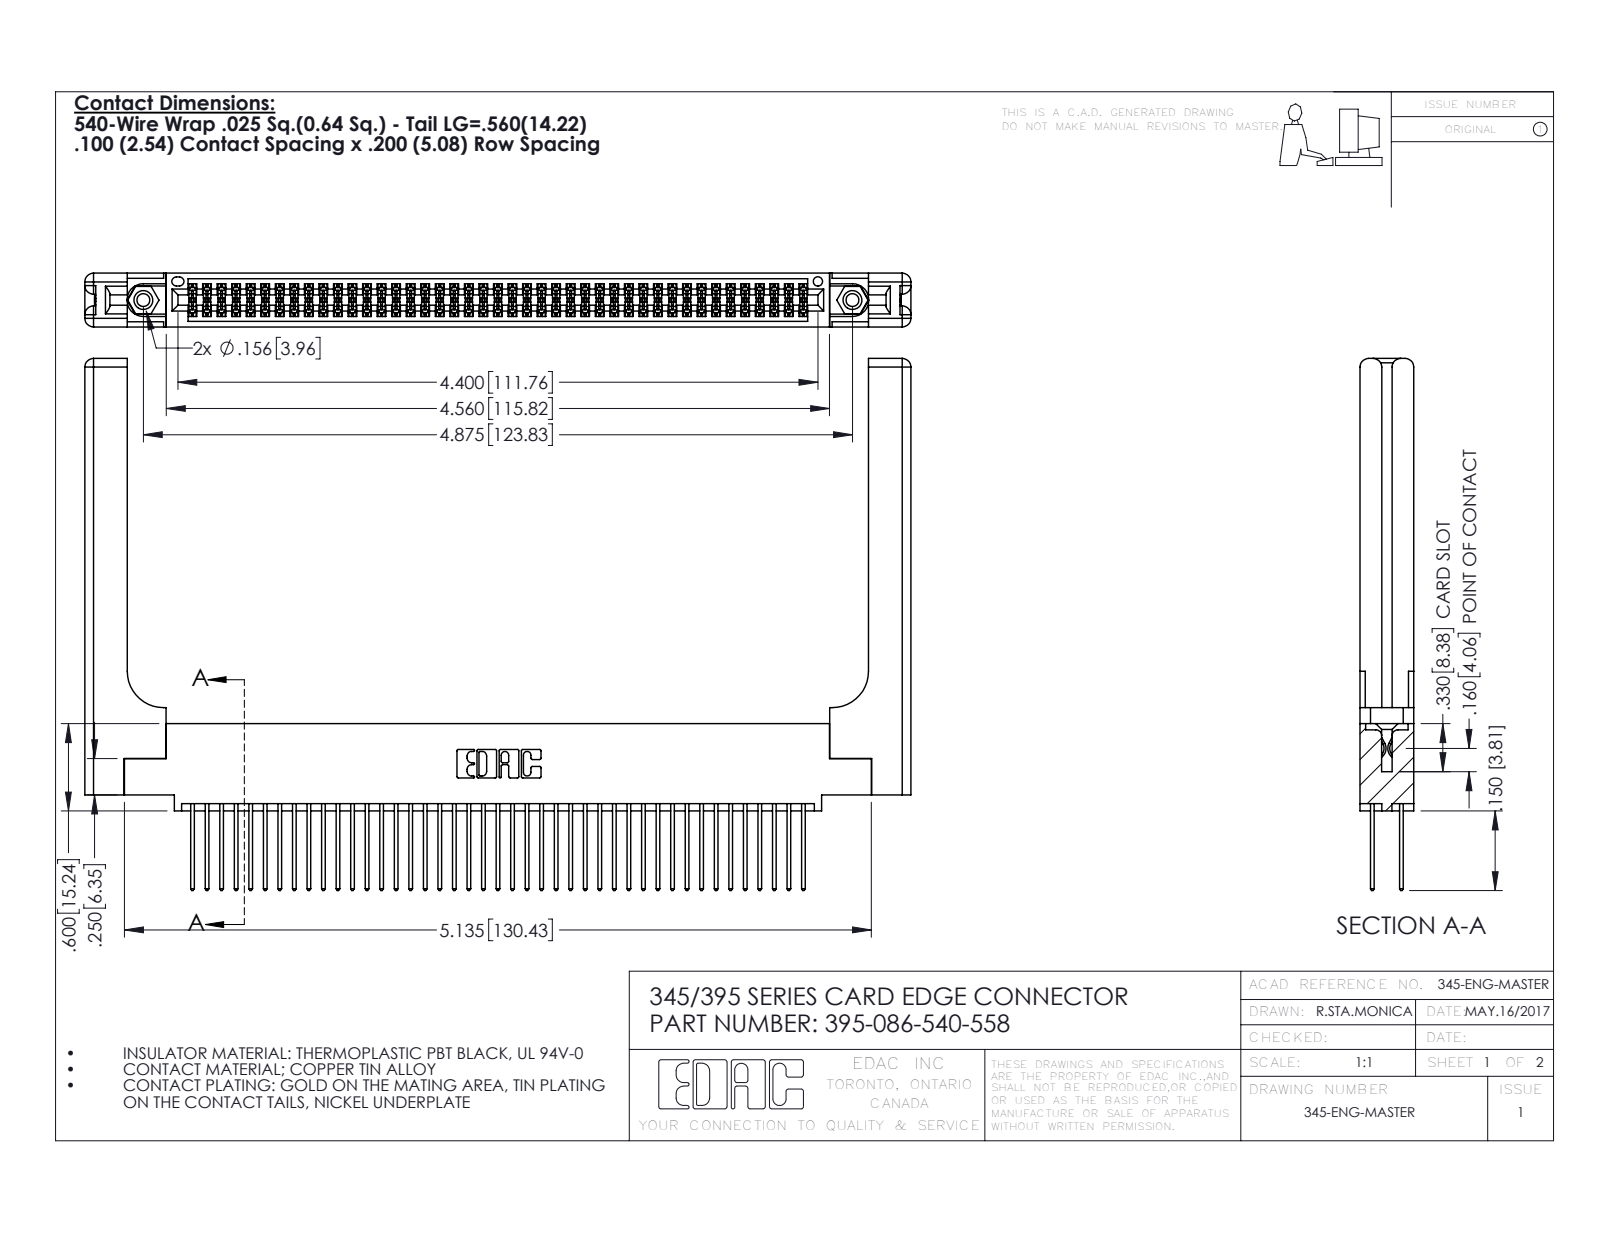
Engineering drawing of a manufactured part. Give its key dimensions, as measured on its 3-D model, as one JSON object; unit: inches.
{"part_name": "345-250-001_345-250-001-102; 345-292-001_345-293-140; 345-220-058_345-220-058; 395-086-540-558 (+1 more)", "step_written_by": "SolidWorks 2016 (CONFIG_CONTROL_DESIGN)", "units": "inches", "bodies": {"solids": 91, "faces": 4686, "planar": 3070, "cylindrical": 1556, "other": 60}, "overall_size": [5.679, 3.657, 0.37], "volume_in3": 1.388, "surface_area_in2": 43.06, "round_holes": [[0.089, 2], [0.125, 2], [0.156, 2], [0.064, 1]], "round_bosses_or_shafts": [[0.155, 2]], "partial_cylinders_radius": [[0.006, 129], [0.01, 86], [0.01, 22], [0.06, 16], [0.007, 6], [0.031, 6], [0.026, 3], [0.014, 2]], "face_to_face_distances": [0.072, 0.298, 0.37, 0.098, 0.272, 0.025, 0.2, 0.225, 0.175, 0.148], "hole_center_spacings": [0.27, 4.639, 4.875]}
